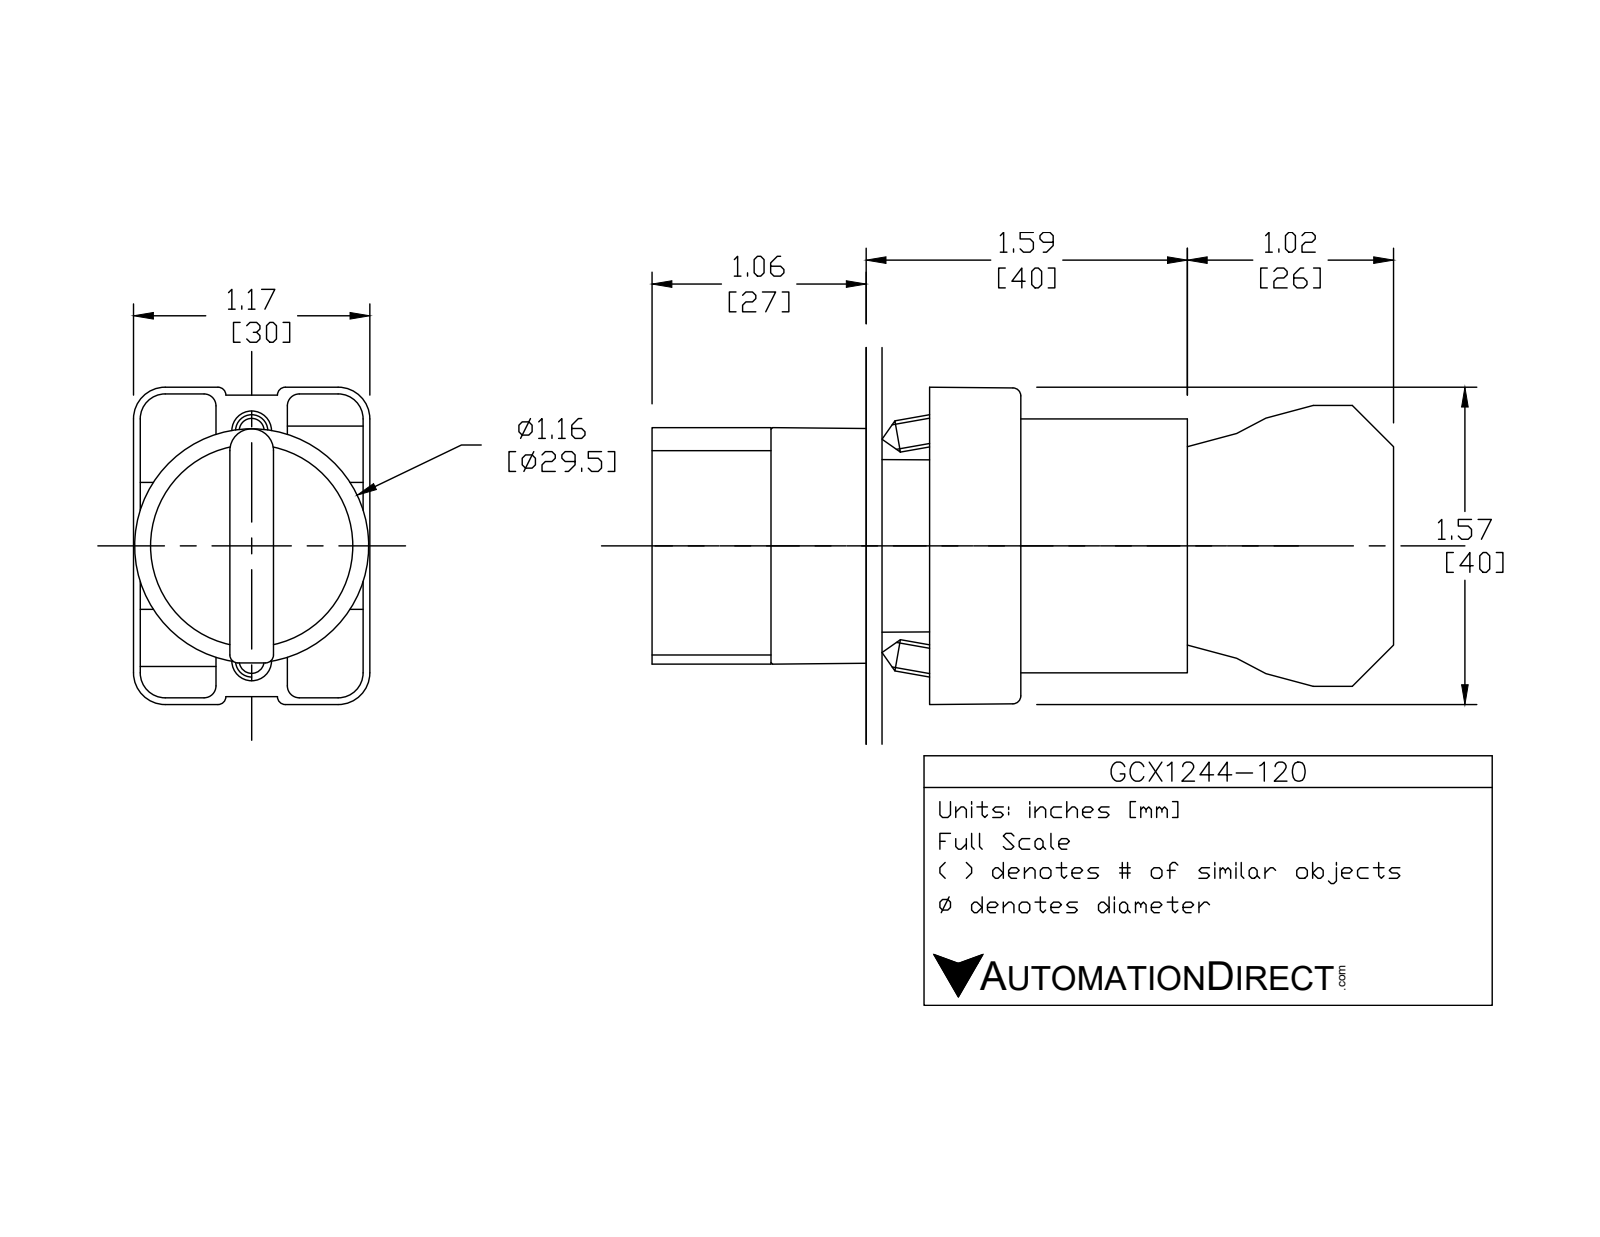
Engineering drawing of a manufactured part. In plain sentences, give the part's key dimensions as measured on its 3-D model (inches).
The part is named "ecx1029; GCX1244-120; ECX1050; ecx1040 (+1 more)". Its 3-D file was written by "SolidWorks 2016 (AUTOMOTIVE_DESIGN)". It is 8 solids with 445 faces: 263 planar, 151 cylindrical and 31 other. Overall it measures 3.653 by 1.581 by 1.177 inches. Its volume is 2.799 cubic inches and its surface area 39 square inches. Round holes: 2 of diameter 0.079, 2 of diameter 0.124, 2 of diameter 0.13, 1 of diameter 0.087, 1 of diameter 0.197, 1 of diameter 0.469, 1 of diameter 0.878, 1 of diameter 0.888, 1 of diameter 1.024. Round bosses or shafts: 4 of diameter 0.157, 1 of diameter 1.175, 1 of diameter 1.004, 1 of diameter 0.945, 1 of diameter 0.856, 1 of diameter 0.78, 1 of diameter 0.504. Partial cylindrical surfaces (rounded edges, fillets, slot ends): 24 of radius 0.059, 12 of radius 0.041, 12 of radius 0.124, 12 of radius 0.157, 9 of radius 0.039, 2 of radius 0.128, 1 of radius 0.02, 1 of radius 0.063. The main face-to-face distances are 0.827, 2.02, 1.193, 0.579, 1.244, 1.171, 0.472, 0.469, 0.031, 0.033. The hole center spacings are 0.236, 0.544, 0.472, 0.49.
